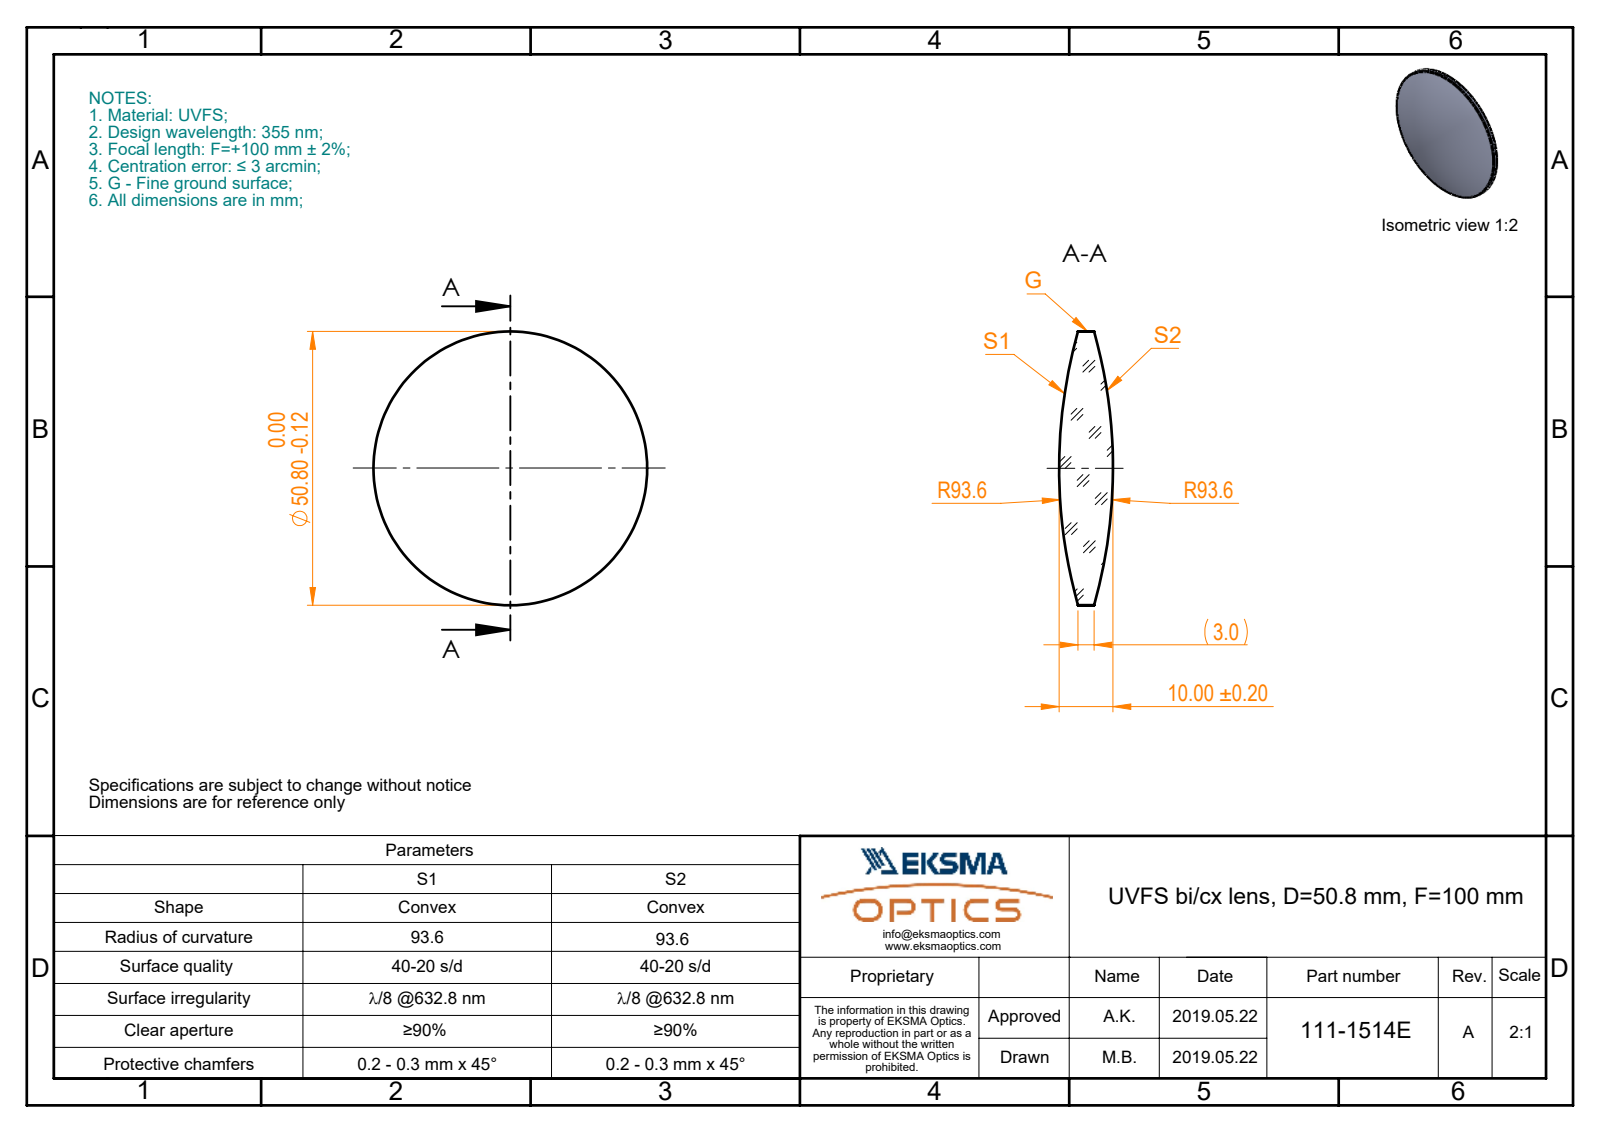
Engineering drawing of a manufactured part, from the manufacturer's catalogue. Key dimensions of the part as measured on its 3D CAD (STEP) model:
Part name (STEP PRODUCT): 111-1514E UVFS bi-cx 50.8 F100
STEP written by: SolidWorks 2017 (CONFIG_CONTROL_DESIGN)
Units: millimetres
Bodies: 1 solid, 6 faces (0 planar, 2 cylindrical, 4 other)
Overall size (bounding box): 50.8 × 50.8 × 10
Volume: 13 193 mm³ · Surface area: 4 606 mm²
Round bosses / shafts (diameter × count): ⌀50.8 ×1
